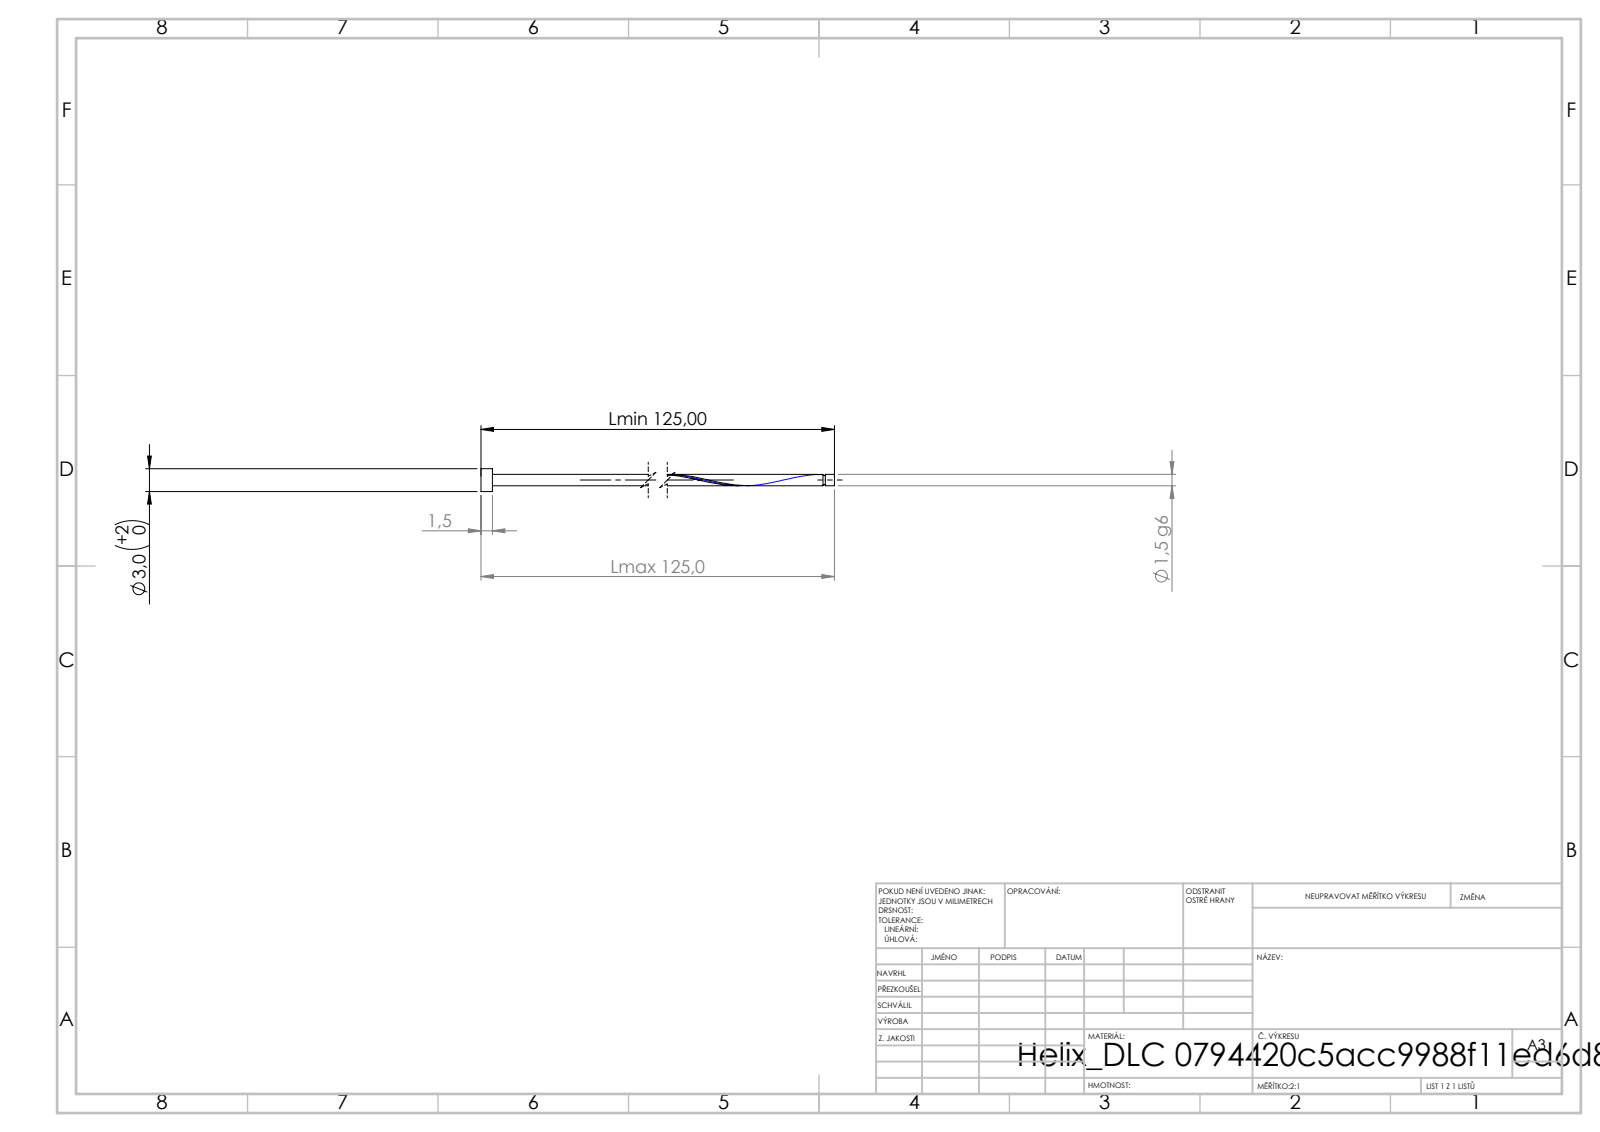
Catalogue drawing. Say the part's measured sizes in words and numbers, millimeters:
Its 3-D file was written by "SolidWorks 2019 (CONFIG_CONTROL_DESIGN)". It is 1 solid with 16 faces: 6 planar, 9 cylindrical and 1 other. Overall it measures 125 by 3 by 3 millimeters. Its volume is 276 cubic millimeters and its surface area 817 square millimeters. Round bosses or shafts: 1 of diameter 3, 1 of diameter 1.5, 1 of diameter 1.2. The main face-to-face distances are 1.5, 125, 123.5, 123.79, 122.29, 1.21, 123.49, 121.99, 1.51, 60.99.
